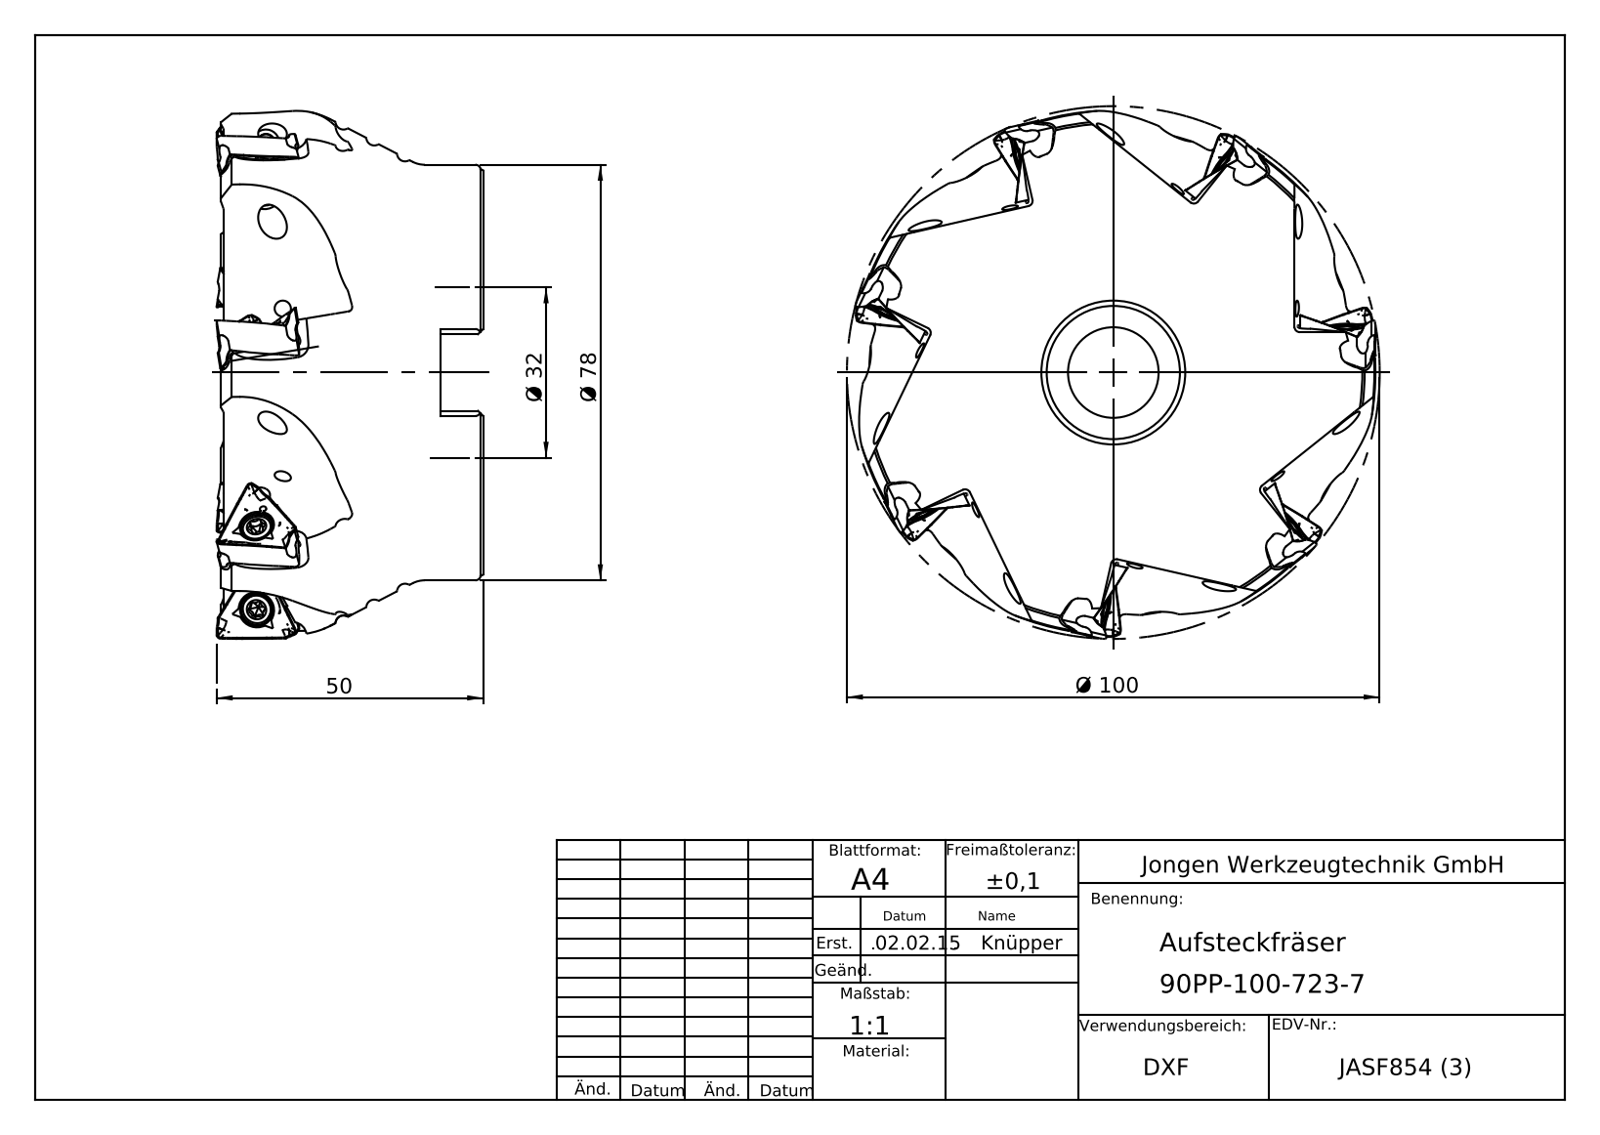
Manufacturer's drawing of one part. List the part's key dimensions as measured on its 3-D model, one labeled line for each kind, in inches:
Part name (STEP PRODUCT): 90PP_100_723_7
STEP written by: SolidWorks 2016 (AUTOMOTIVE_DESIGN)
Units: inches
Bodies: 1 solid, 542 faces (146 planar, 214 cylindrical, 182 other)
Overall size (bounding box): 3.961 × 3.936 × 1.97
Volume: 16.02 in³ · Surface area: 60.76 in²
Round holes (diameter × count): ⌀0.118 ×7, ⌀0.669 ×1, ⌀0.984 ×1, ⌀1.26 ×1, ⌀1.266 ×1, ⌀1.272 ×1
Round bosses / shafts (diameter × count): ⌀3.071 ×1
Partial cylindrical surfaces — rounded edges, fillets, slot ends (radius × count): R0.049 ×56, R0.098 ×21, R0.079 ×14, R0.016 ×7, R0.039 ×7, R0.787 ×7
Main face-to-face distances: 1.917, 0.313, 1.604, 0.984, 0.671, 0.933, 0.567, 0.512, 1.093, 1.406
